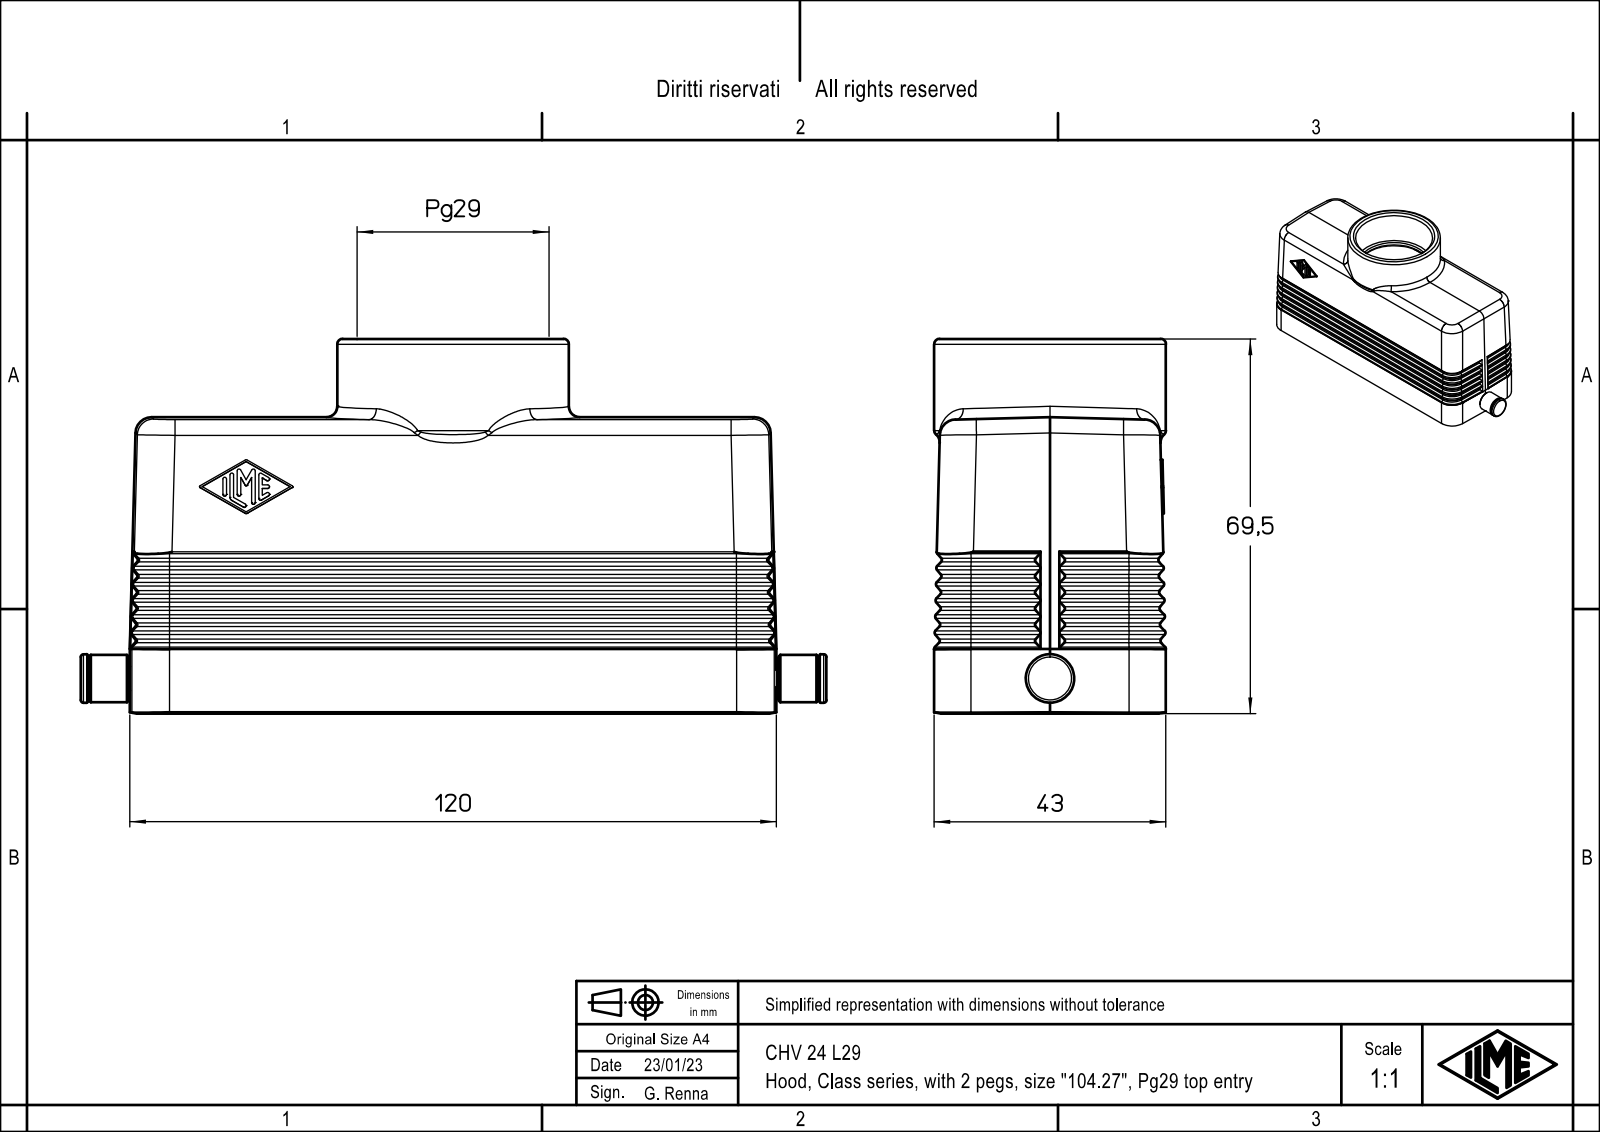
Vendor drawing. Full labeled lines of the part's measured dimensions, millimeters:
Part name (STEP PRODUCT): CH Tüllengehäuse für einen Einsatz Teil 4
STEP written by: Autodesk Inventor 7 (AUTOMOTIVE_DESIGN)
Units: millimetres
Bodies: 1 solid, 497 faces (184 planar, 115 cylindrical, 198 other)
Overall size (bounding box): 135 × 68 × 43
Volume: 75 313 mm³ · Surface area: 47 187 mm²
Round holes (diameter × count): ⌀30.32 ×1, ⌀35.48 ×1
Round bosses / shafts (diameter × count): ⌀39 ×1, ⌀9 ×1, ⌀5 ×1
Partial cylindrical surfaces — rounded edges, fillets, slot ends (radius × count): R0.25 ×14, R3 ×8, R2 ×4, R6 ×4, R5.3 ×2, R1.5 ×1
Main face-to-face distances: 3, 40, 37, 43, 11.5, 8.5, 1.77, 117, 5.3, 120
